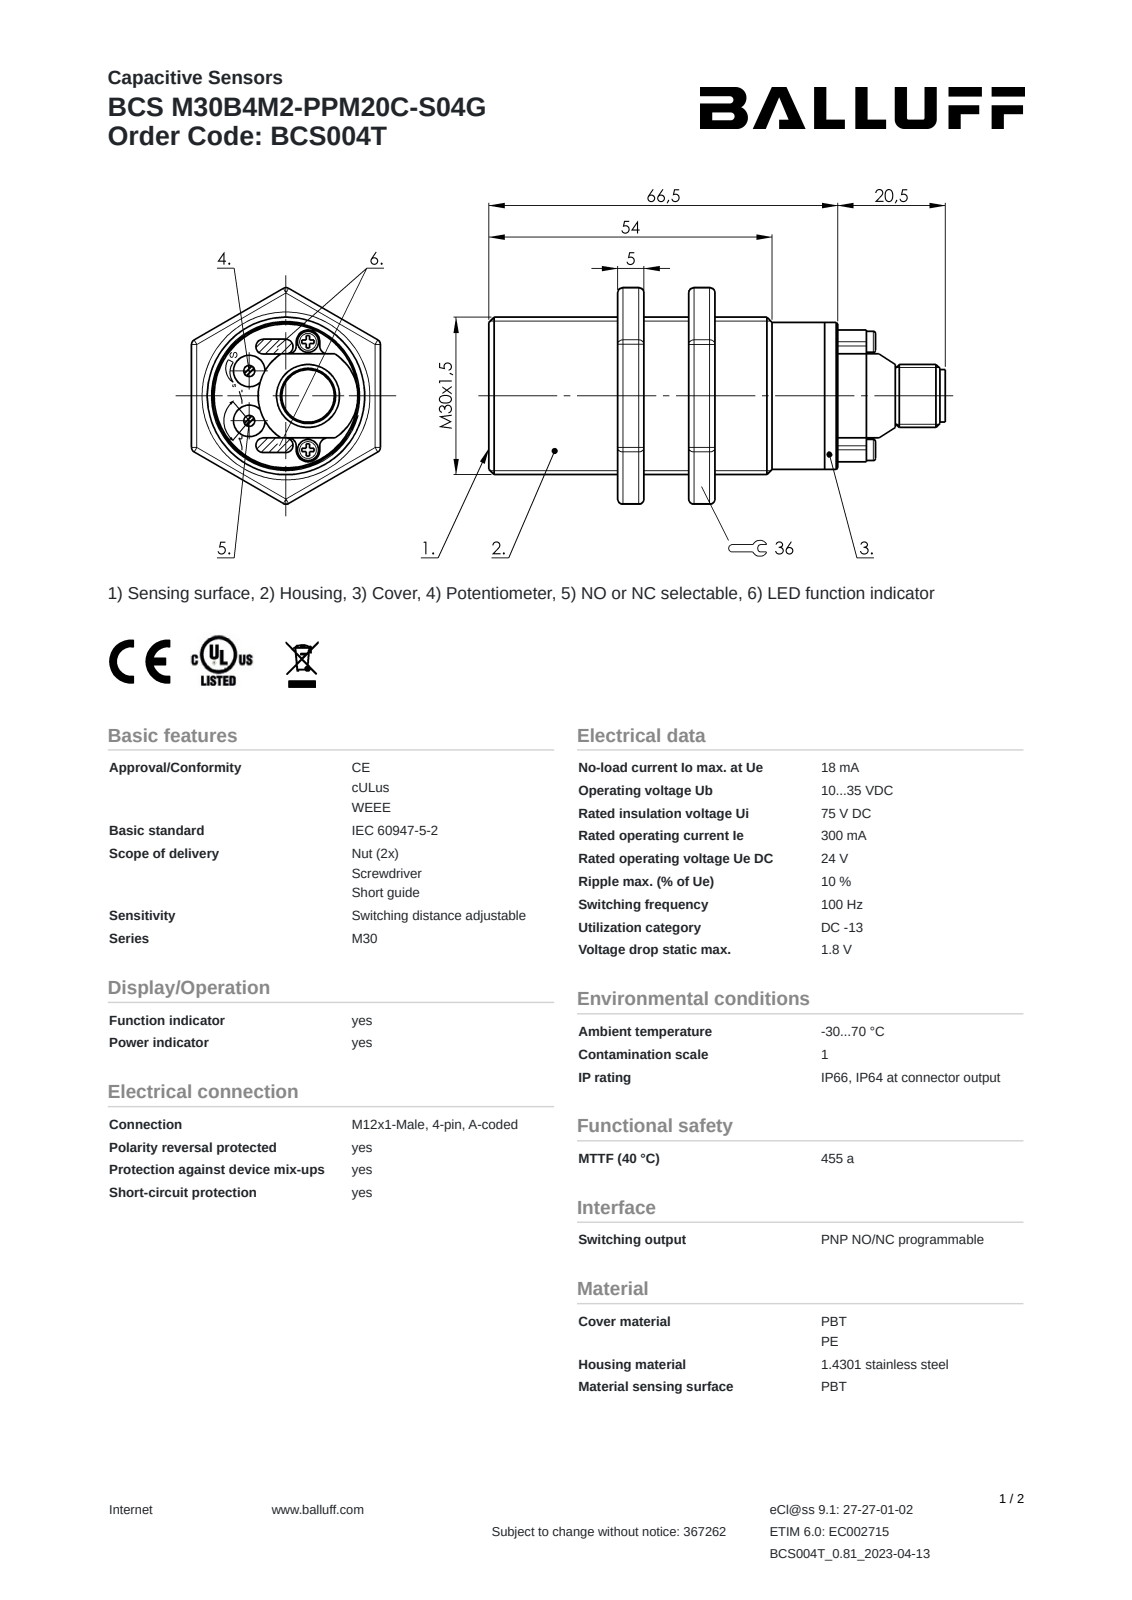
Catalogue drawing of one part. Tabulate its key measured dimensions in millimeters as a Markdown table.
| quantity | value |
| --- | --- |
| part name | BCS004T |
| STEP written by | SolidWorks 2021 (CONFIG_CONTROL_DESIGN) |
| units | millimeters |
| bodies | 3 solids, 158 faces (86 planar, 33 cylindrical, 39 other) |
| overall size | 87 × 41.6 × 36 |
| volume | 53 750 mm³ |
| surface area | 12 590 mm² |
| round holes (diameter × count) | 2.5 × 2, 5 × 2, 8.3 × 1, 28.4 × 1 |
| round bosses / shafts (diameter × count) | 1 × 4, 4 × 2, 30 × 1, 28 × 1, 27.8 × 1, 12 × 1, 10.4 × 1 |
| partial cylindrical surfaces (radius × count) | 1.3 × 4, 1.5 × 4, 2.3 × 2, 0.6 × 1, 9.2 × 1, 9.5 × 1 |
| main face-to-face distances | 8, 5, 36, 37.5, 29.5, 13, 3, 32.5, 24.5, 29 |
| hole center spacings | 8.5, 12.2, 4.2, 9.5 |
